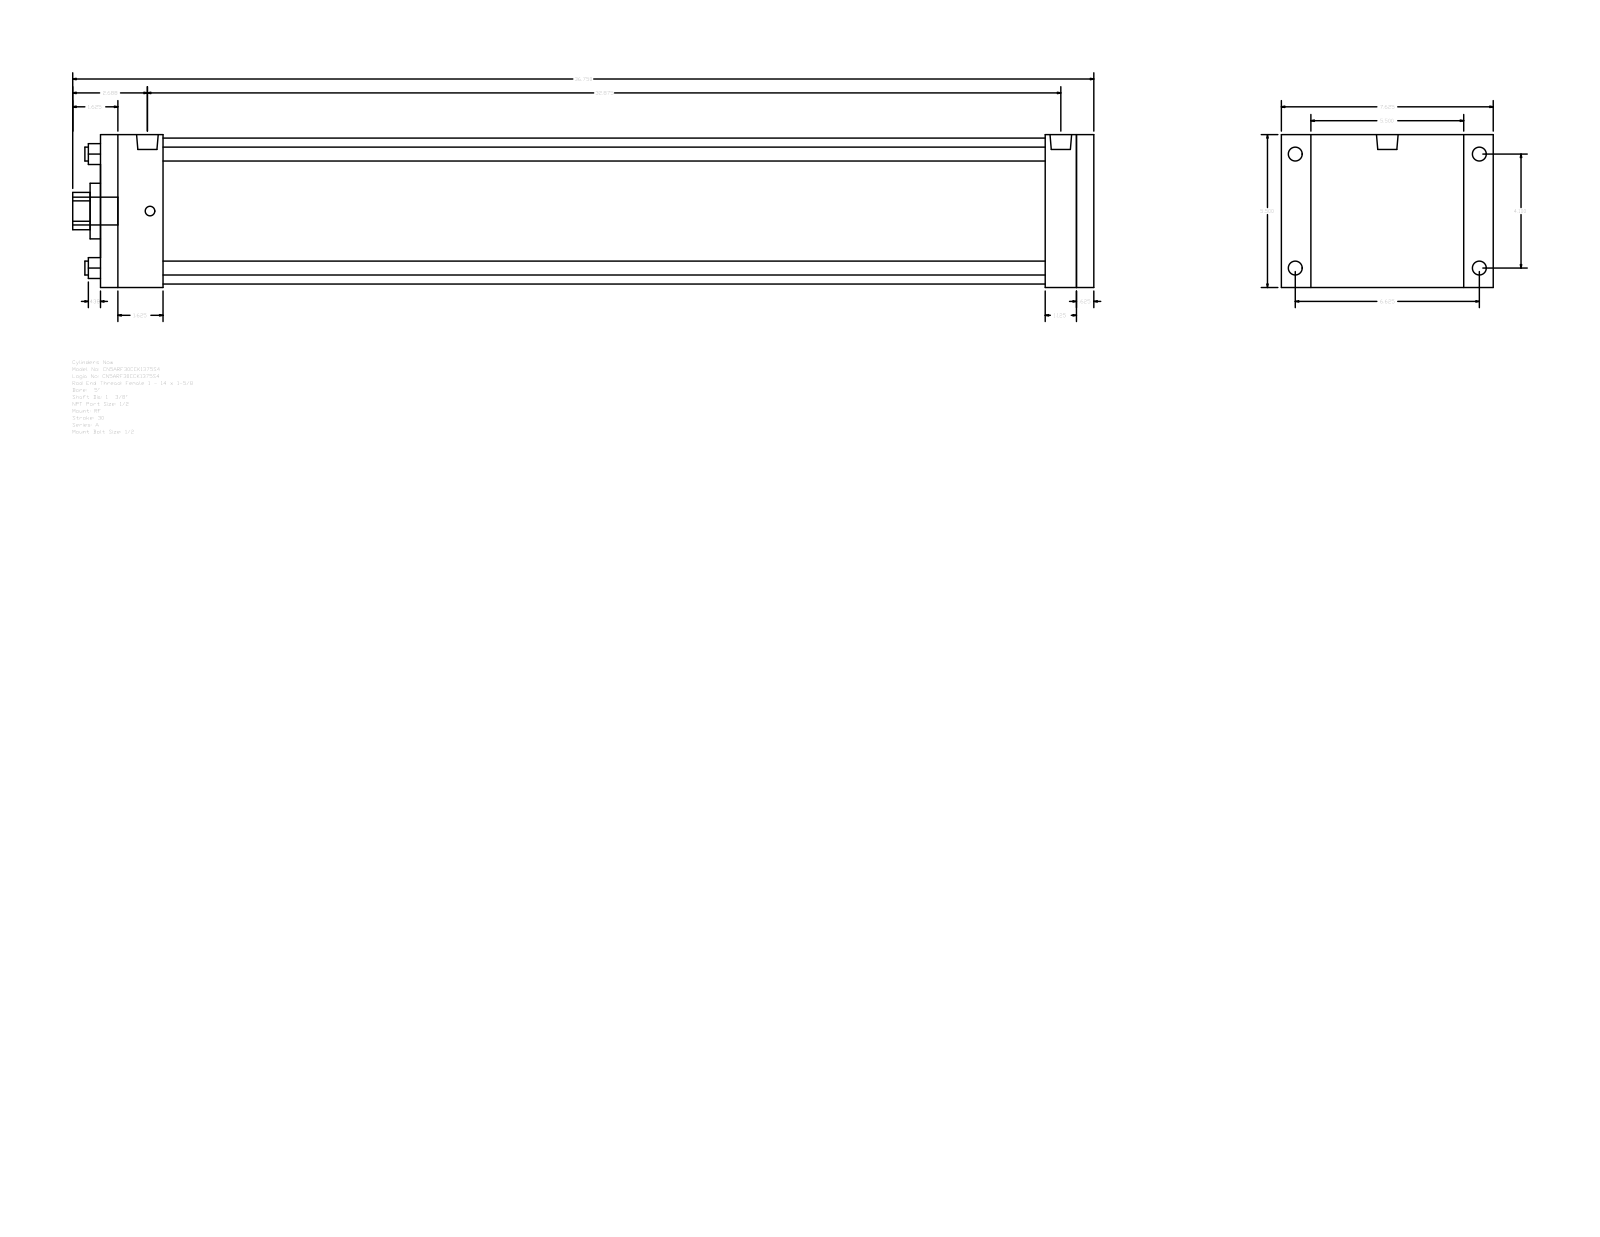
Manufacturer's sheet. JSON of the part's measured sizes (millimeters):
{"part_name": "A_RF__0500_1.375", "step_written_by": "GSSL Pune (CONFIG_CONTROL_DESIGN)", "units": "millimeters", "bodies": {"solids": 0, "faces": 92, "planar": 64, "cylindrical": 28, "other": 0}, "overall_size": [933.45, 193.68, 139.7], "round_holes": [[12.7, 4], [34.92, 1], [50.8, 1], [133.35, 1]], "round_bosses_or_shafts": [[12.7, 4], [8.73, 4], [19.77, 2], [25.4, 1]], "partial_cylinders_radius": [[17.06, 1]], "face_to_face_distances": [139.7, 908.05, 15.87, 892.18, 28.58, 57.15, 835.03, 850.9, 863.6, 806.45], "hole_center_spacings": [73.64, 104.14, 147.28]}
